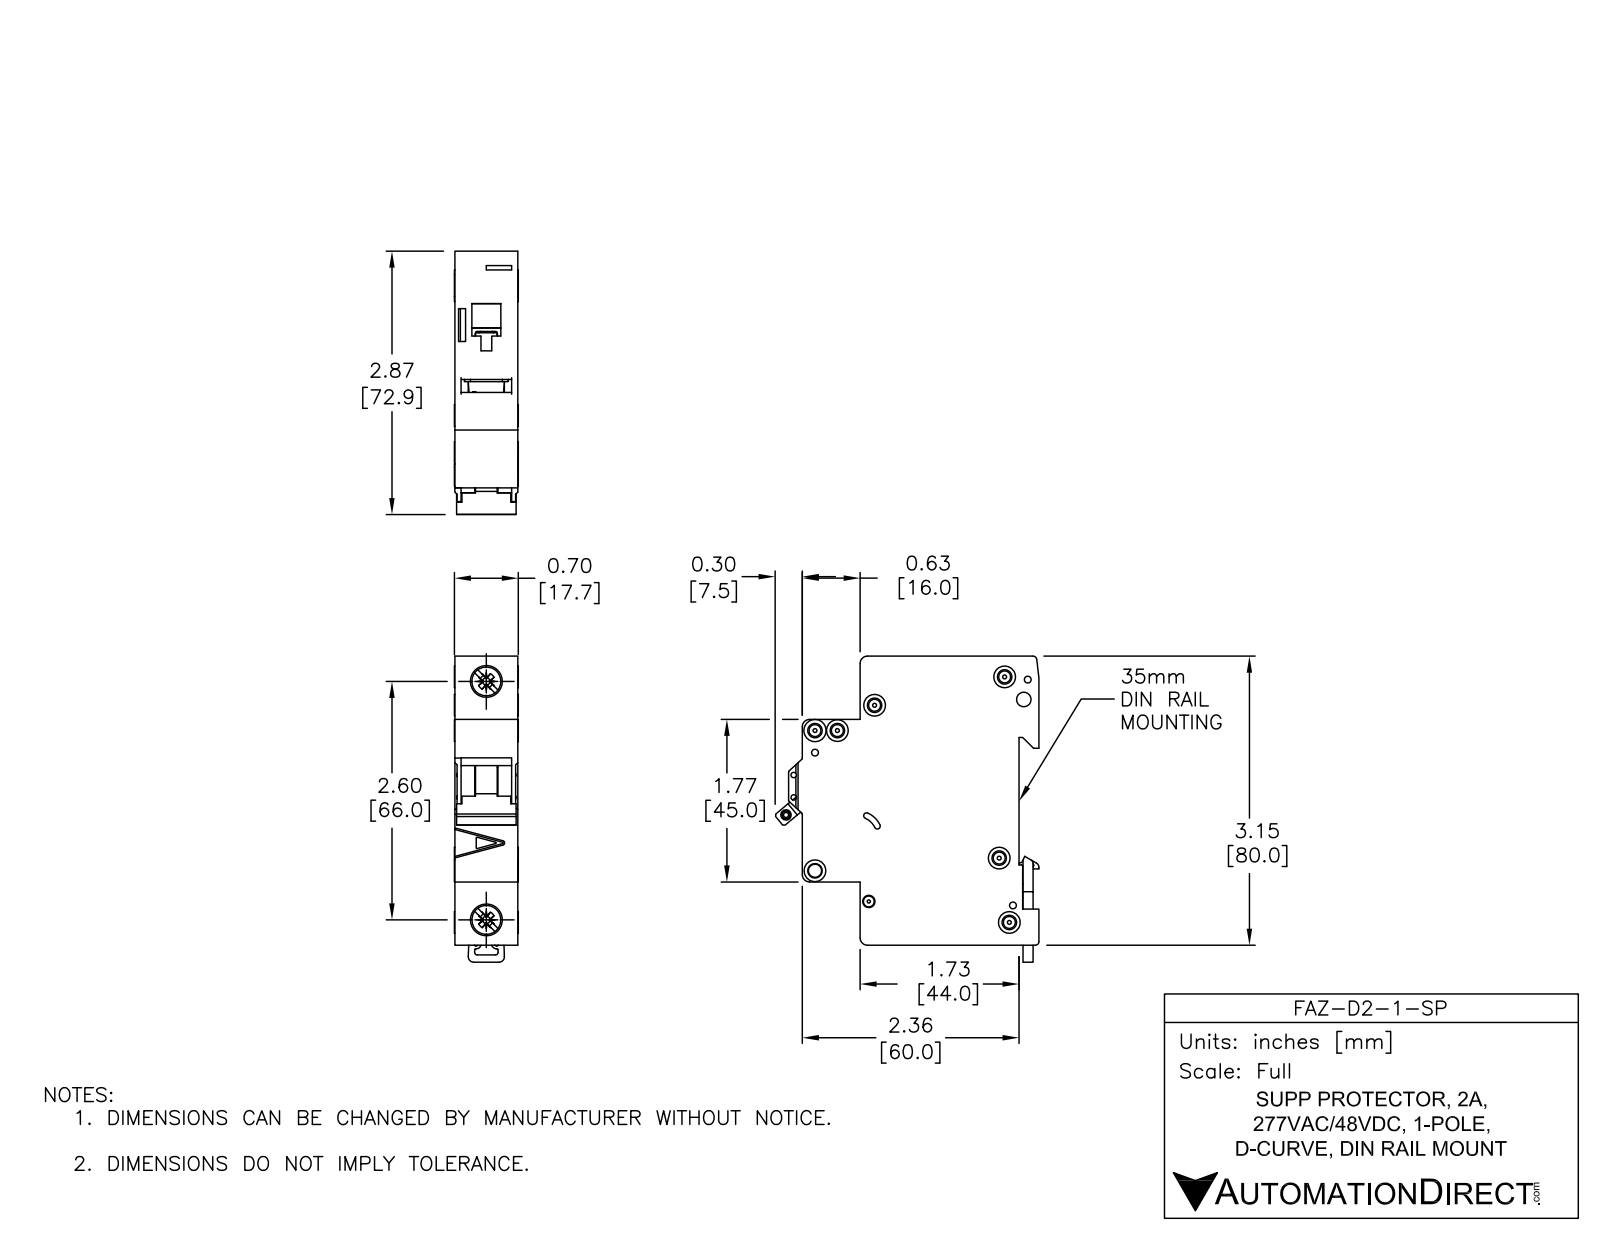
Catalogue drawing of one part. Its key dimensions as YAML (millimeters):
part_name: "FAZ-D2-1-SP"
step_written_by: "SolidWorks 2014 (AUTOMOTIVE_DESIGN)"
units: millimeters
bodies: {solids: 5, faces: 558, planar: 235, cylindrical: 202, other: 121}
overall_size: [84.78, 73.04, 17.7]
volume: 74935
surface_area: 19545
round_holes:
  - {diameter: 3.6, count: 6}
  - {diameter: 1.9, count: 3}
  - {diameter: 1.09, count: 2}
  - {diameter: 1.5, count: 2}
  - {diameter: 4, count: 2}
  - {diameter: 7.15, count: 2}
  - {diameter: 2.15, count: 1}
  - {diameter: 2.2, count: 1}
  - {diameter: 2.55, count: 1}
  - {diameter: 3.3, count: 1}
  - {diameter: 3.4, count: 1}
round_bosses_or_shafts:
  - {diameter: 6, count: 4}
  - {diameter: 8.2, count: 2}
  - {diameter: 2.5, count: 1}
partial_cylinders:
  - {radius: 0.25, count: 30}
  - {radius: 0.5, count: 13}
  - {radius: 2, count: 8}
  - {radius: 0.2, count: 5}
  - {radius: 1, count: 4}
  - {radius: 0.8, count: 2}
  - {radius: 3, count: 2}
  - {radius: 1.5, count: 1}
face_to_face_distances: [17.5, 79.48, 5.5, 49.5, 44, 65.5, 60, 16, 1.75, 15.75]
hole_center_spacings: [6.2, 13.64, 4.81, 5.19, 5.61, 6.1, 6.44, 8.19]
